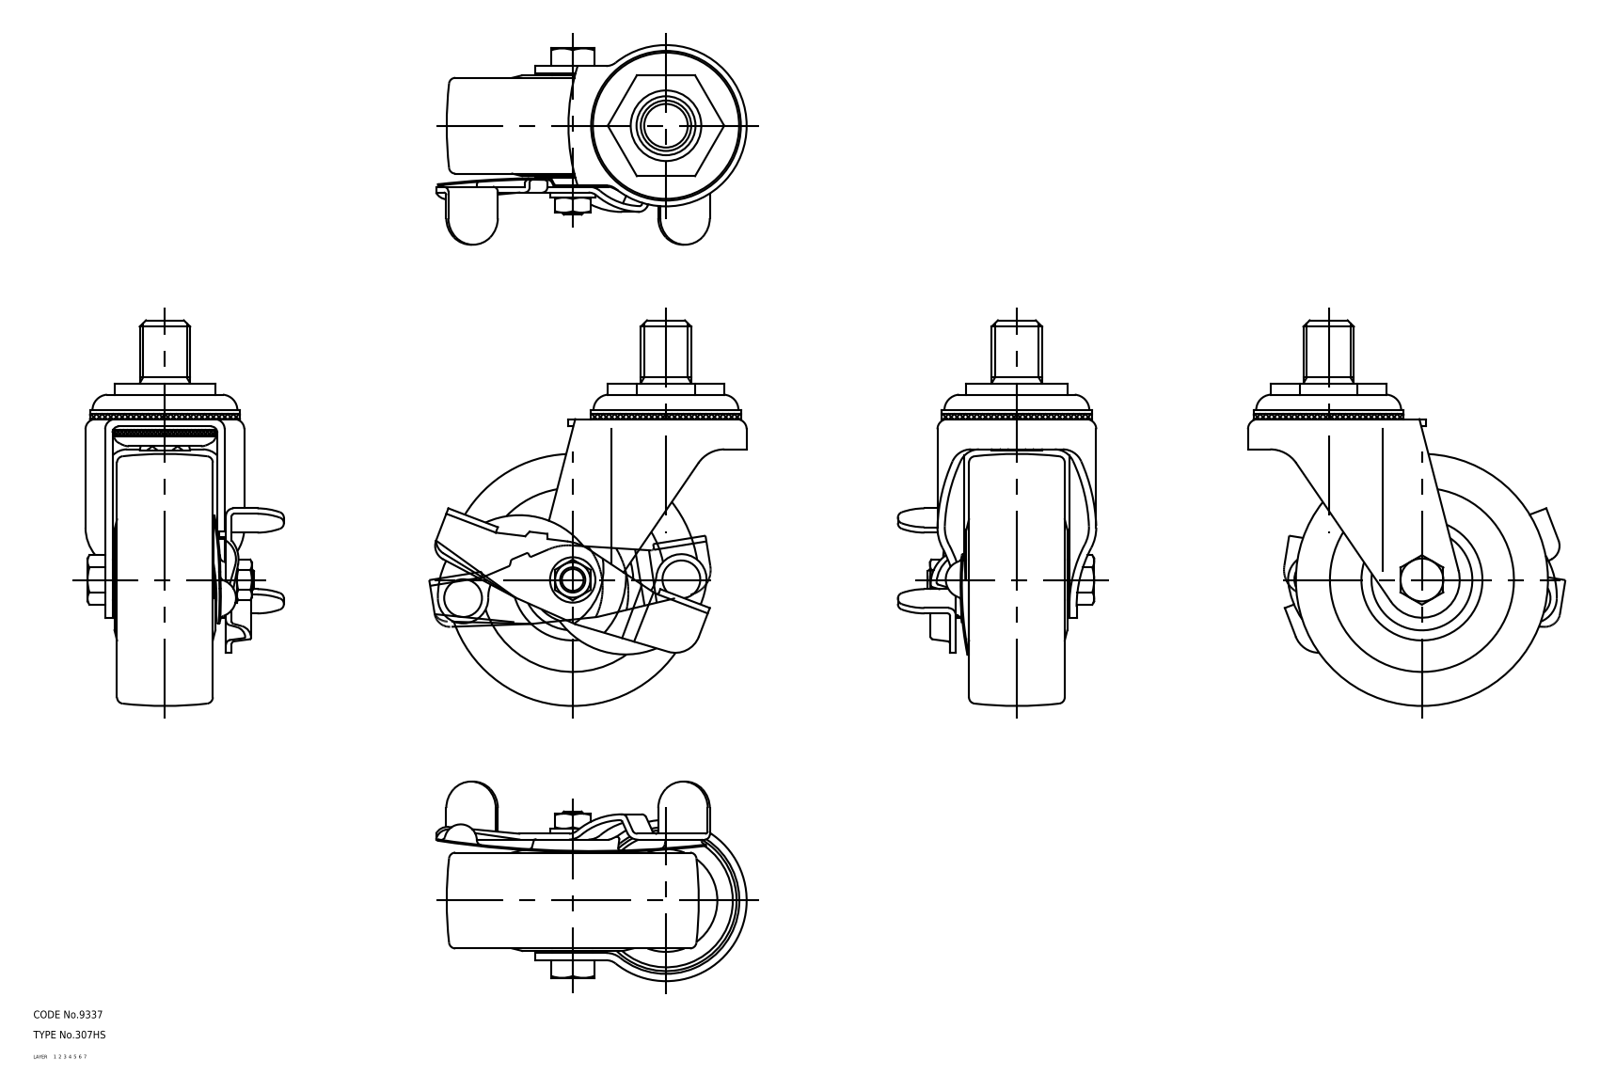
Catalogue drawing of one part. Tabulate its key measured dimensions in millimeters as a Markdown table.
| quantity | value |
| --- | --- |
| part name | 67132217; 67132230; 67132243; 67132256 (+2 more) |
| STEP written by | CADfix (AUTOMOTIVE_DESIGN) |
| units | millimeters |
| bodies | 6 solids, 332 faces (0 planar, 0 cylindrical, 332 other) |
| overall size | 153 × 123.6 × 78.7 |
| volume | 342 258 mm³ |
| surface area | 84 317 mm² |
